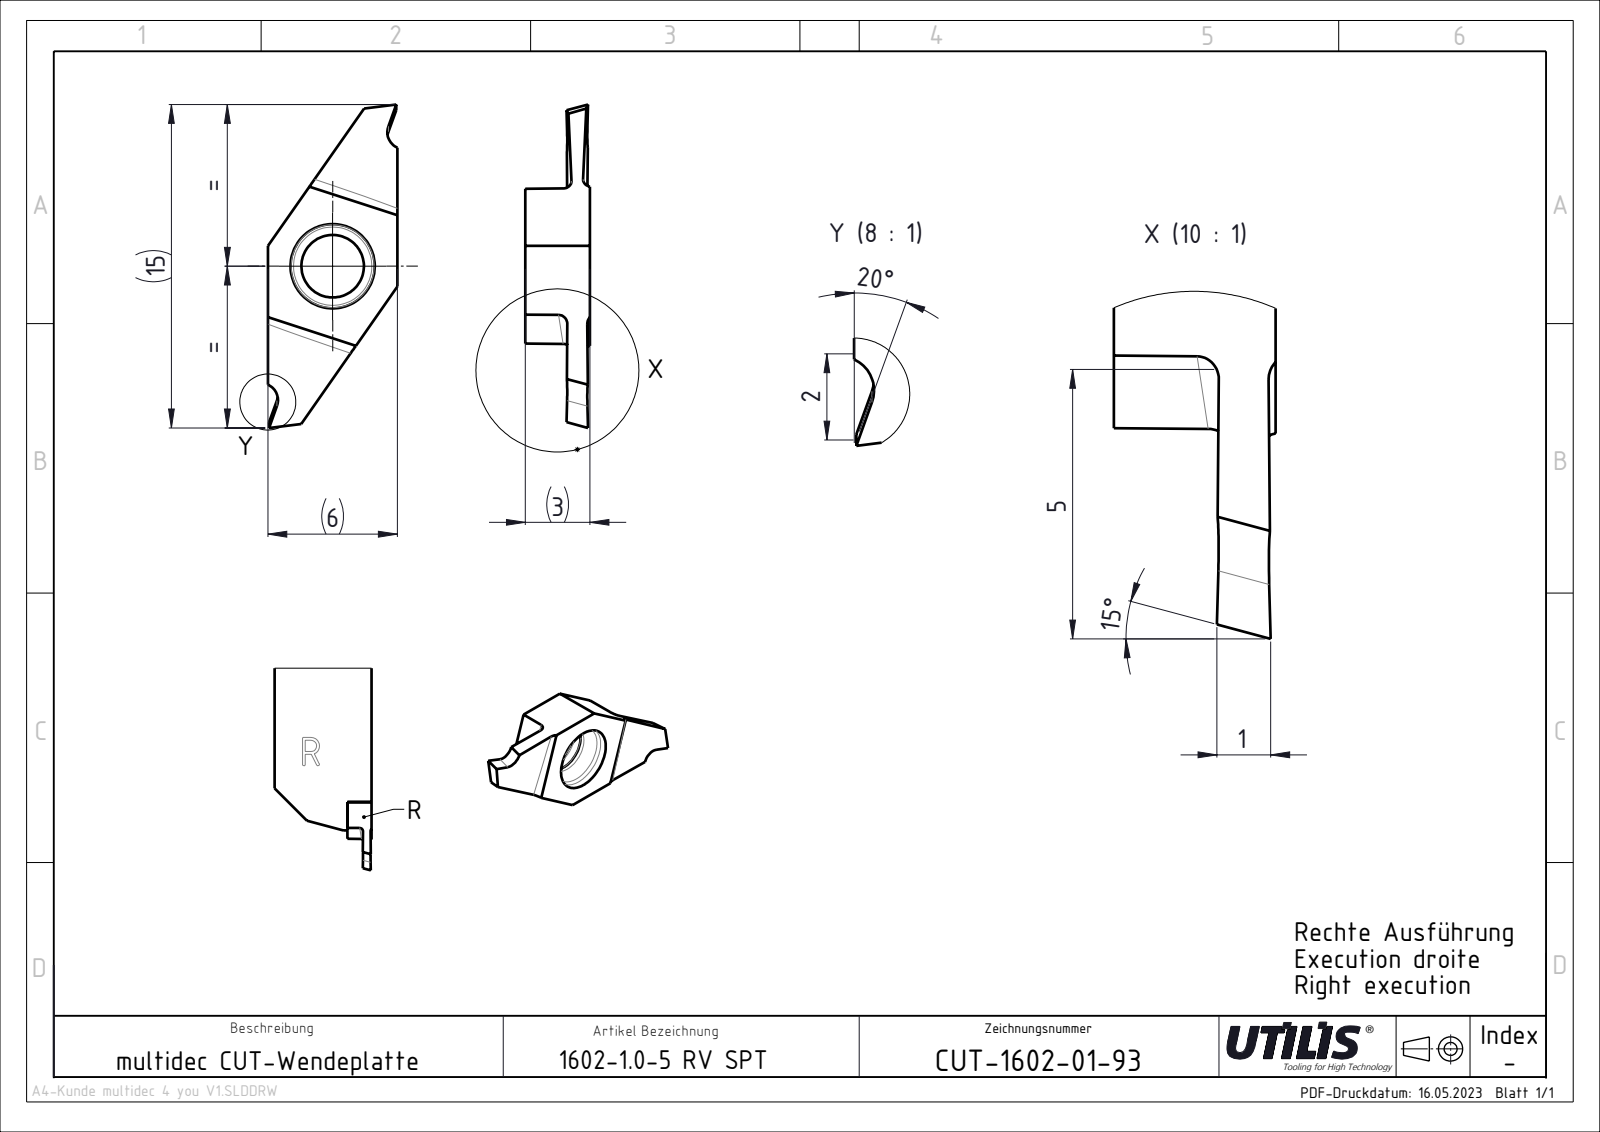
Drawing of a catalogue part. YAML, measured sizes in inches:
part_name: "CUT-1602-01-CUT-1602-CUT-1602-01-93 stp"
step_written_by: "SolidWorks 2022 (AUTOMOTIVE_DESIGN)"
units: inches
bodies: {solids: 1, faces: 19, planar: 14, cylindrical: 5, other: 0}
overall_size: [0.591, 0.236, 0.118]
volume: 0.006
surface_area: 0.324
round_holes:
  - {diameter: 0.114, count: 1}
partial_cylinders:
  - {radius: 0.016, count: 4}
face_to_face_distances: [0.236, 0.118, 0.033]
